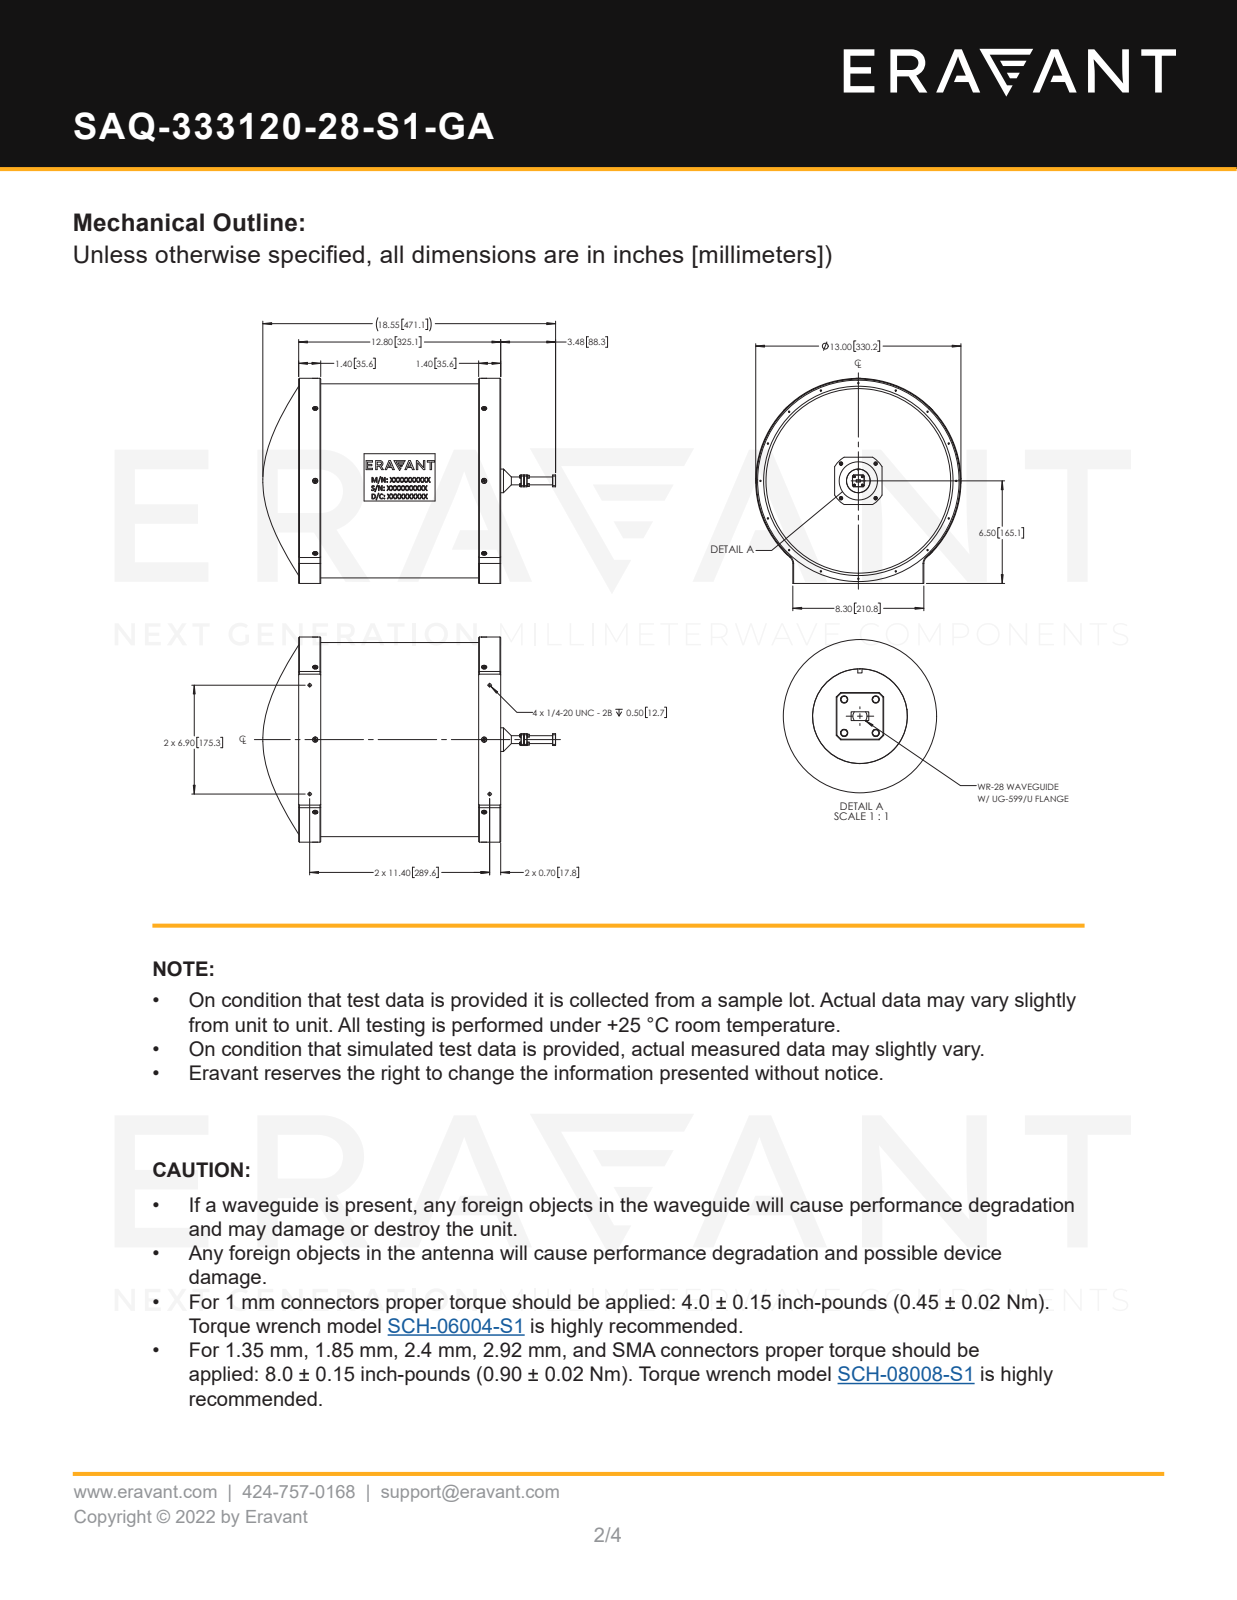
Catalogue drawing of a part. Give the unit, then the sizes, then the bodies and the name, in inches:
Units: inches
Overall size (bounding box): 18.545 × 13 × 13
Round holes (diameter × count): ⌀0.089 ×16, ⌀0.129 ×16, ⌀0.177 ×12, ⌀0.085 ×4, ⌀0.112 ×4, ⌀0.116 ×4, ⌀0.12 ×4, ⌀0.136 ×4, ⌀0.188 ×4, ⌀0.201 ×4, ⌀0.219 ×4, ⌀0.328 ×1
Round bosses / shafts (diameter × count): ⌀0.112 ×16, ⌀0.163 ×12, ⌀0.183 ×8, ⌀0.18 ×4, ⌀0.19 ×2, ⌀12.765 ×1, ⌀12.75 ×1, ⌀12.3 ×1
Partial cylindrical surfaces — rounded edges, fillets, slot ends (radius × count): R0.5 ×2, R1.75 ×1, R6.5 ×1
Main face-to-face distances: 11.4, 1.4, 12.55, 1.15, 11.15, 10, 0.05, 12.6, 1.2, 11.2
Hole centre spacings: 6.889, 4.745, 6.2, 10.7, 2.419, 2.419, 4.805, 5.22
Volume: 1 663 in³ · Surface area: 877.2 in²
Bodies: 18 solids, 1829 faces (863 planar, 362 cylindrical, 604 other)
Part name (STEP PRODUCT): SAQ-333120-28-S1-GA
STEP written by: SolidWorks 2021 (CONFIG_CONTROL_DESIGN)
